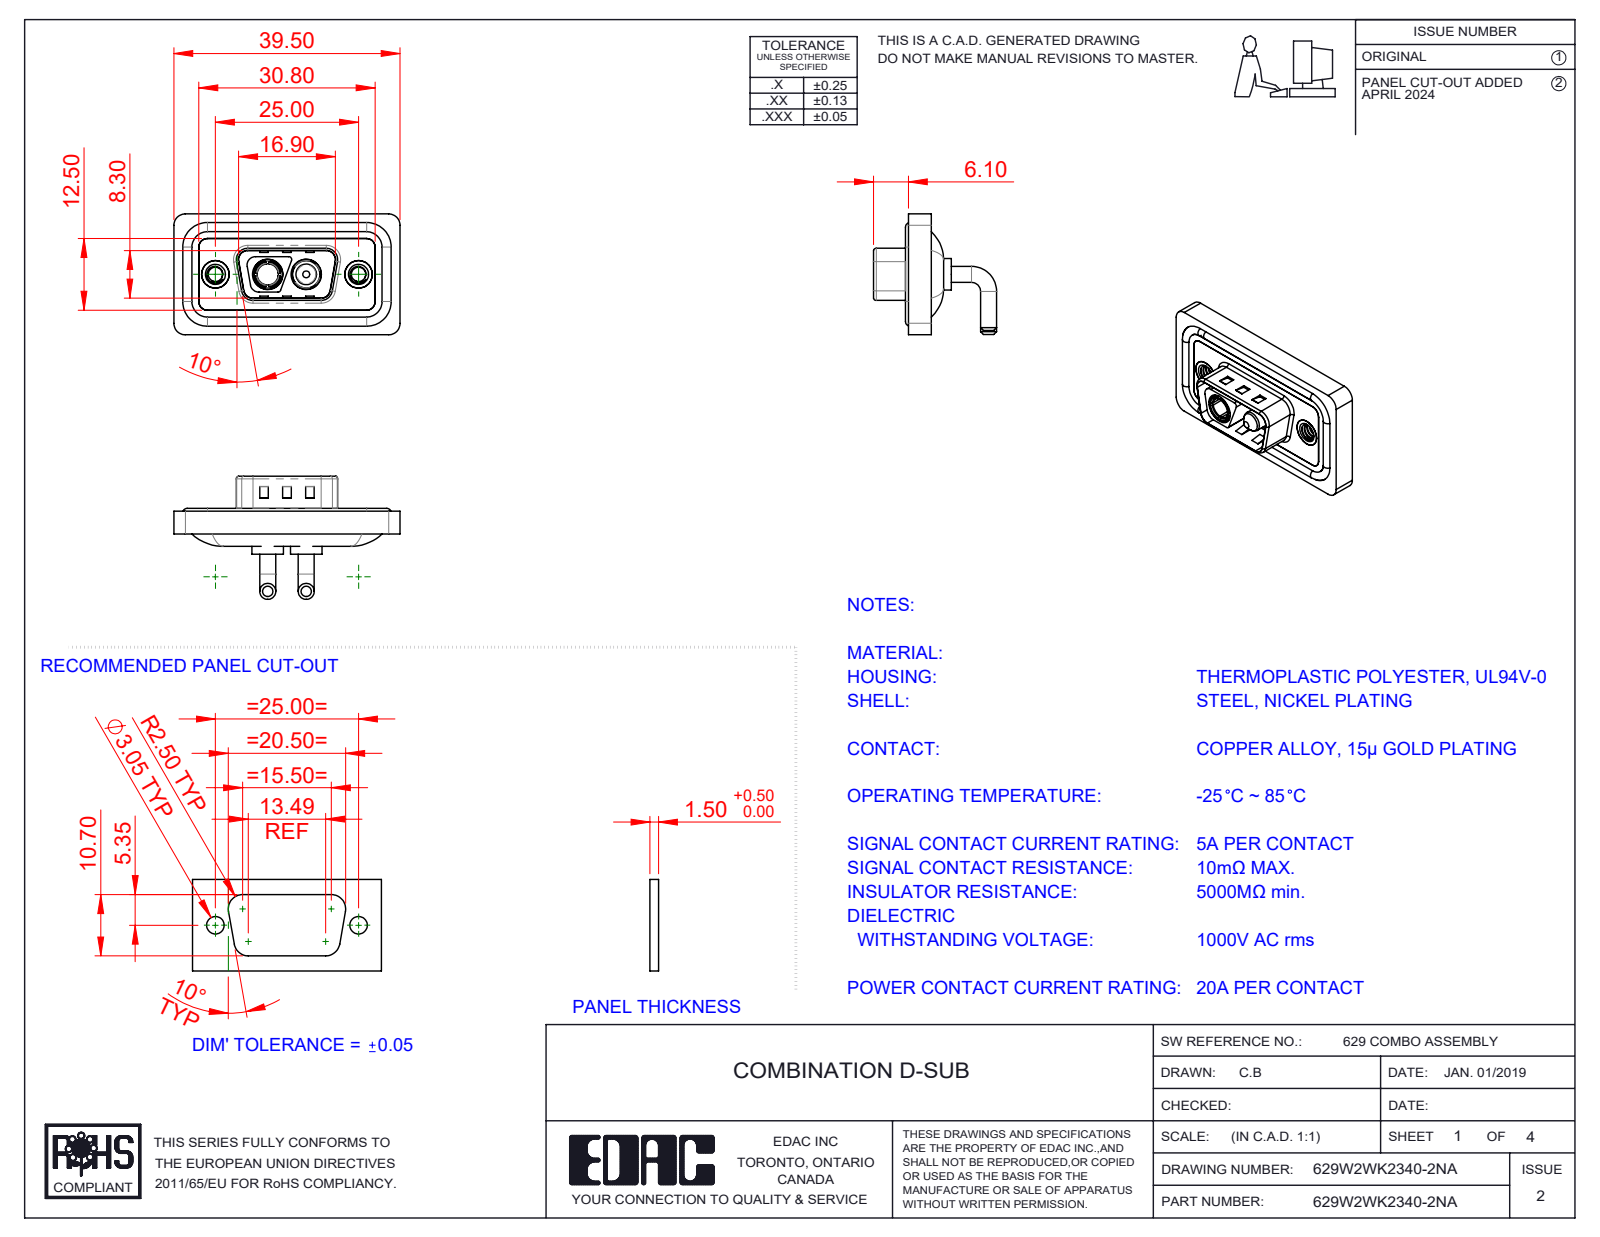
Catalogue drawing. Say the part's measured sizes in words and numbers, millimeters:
The part is named "629Combo Threaded Rivet_A; Power Socket_20A RA; Power Pin_20A RA; 629Combo Shell Front_09 Contacts (+4 more)". Its 3-D file was written by "SolidWorks 2023 (CONFIG_CONTROL_DESIGN)". It is 11 solids with 536 faces: 189 planar, 229 cylindrical and 118 other. Overall it measures 39.5 by 21.5 by 21.1 millimeters. Its volume is 4 686 cubic millimeters and its surface area 7 536 square millimeters. Round holes: 2 of diameter 2.5, 2 of diameter 4, 2 of diameter 4.8, 2 of diameter 4.85, 2 of diameter 5, 2 of diameter 5.3, 1 of diameter 3.7. Round bosses or shafts: 4 of diameter 2.8, 4 of diameter 1.6, 2 of diameter 5.5, 2 of diameter 5.2, 2 of diameter 4.9, 2 of diameter 4.75, 2 of diameter 3.75, 1 of diameter 4.96. Partial cylindrical surfaces (rounded edges, fillets, slot ends): 20 of radius 1.5, 18 of radius 2, 10 of radius 0.5, 8 of radius 1.6, 4 of radius 0.25, 4 of radius 0.6, 4 of radius 0.65, 4 of radius 0.9. The main face-to-face distances are 0.4, 2.9, 1.1, 0.8, 2.1, 2.5, 3.1, 1.6, 4.5, 1.5. The hole center spacings are 9.14, 15.86, 6.72, 25.
